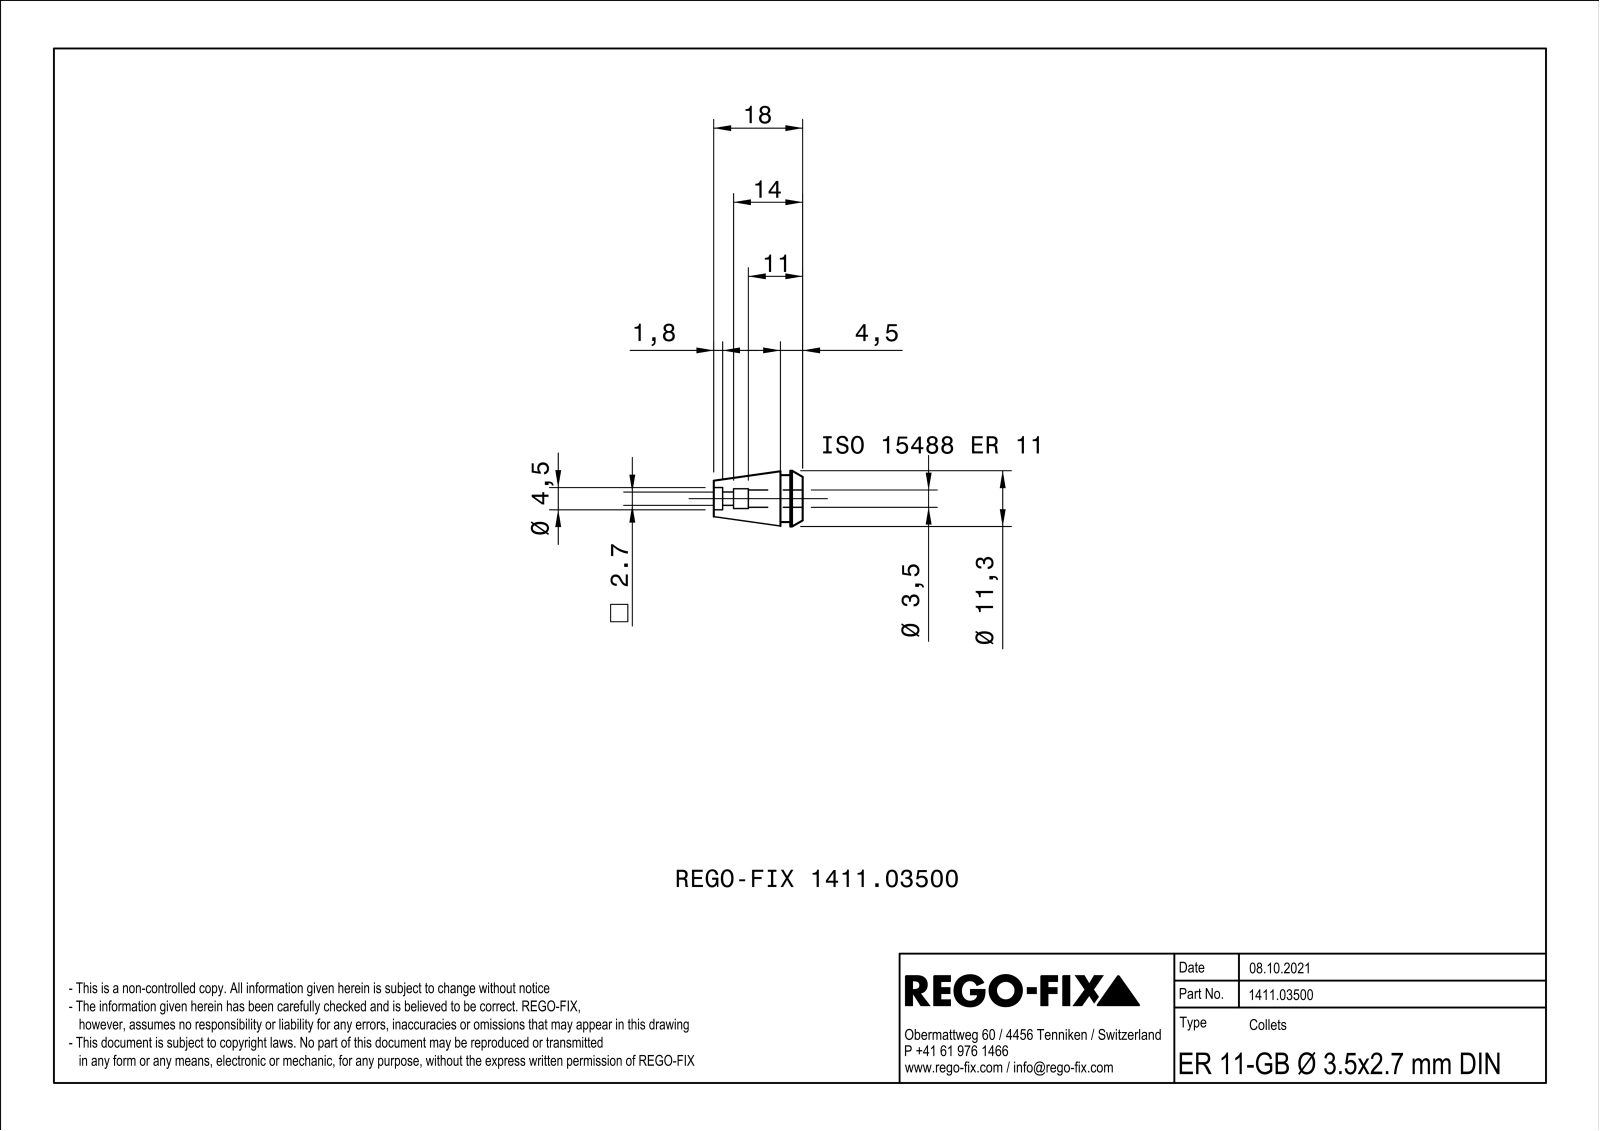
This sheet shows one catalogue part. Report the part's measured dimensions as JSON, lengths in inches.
{"part_name": "NOCUT", "step_written_by": "SIEMENS PLM Software Solid Edge ST10 (AUTOMOTIVE_DESIGN)", "units": "inches", "bodies": {"solids": 1, "faces": 144, "planar": 68, "cylindrical": 32, "other": 44}, "overall_size": [0.709, 0.444, 0.444], "volume_in3": 0.054, "surface_area_in2": 2.302, "round_holes": [[0.138, 1], [0.177, 1]], "round_bosses_or_shafts": [[0.445, 1], [0.374, 1]], "partial_cylinders_radius": [[0.061, 1], [0.079, 1]], "face_to_face_distances": [0.02, 0.098, 0.531, 0.177, 0.079, 0.709, 0.61, 0.059, 0.046, 0.066]}
